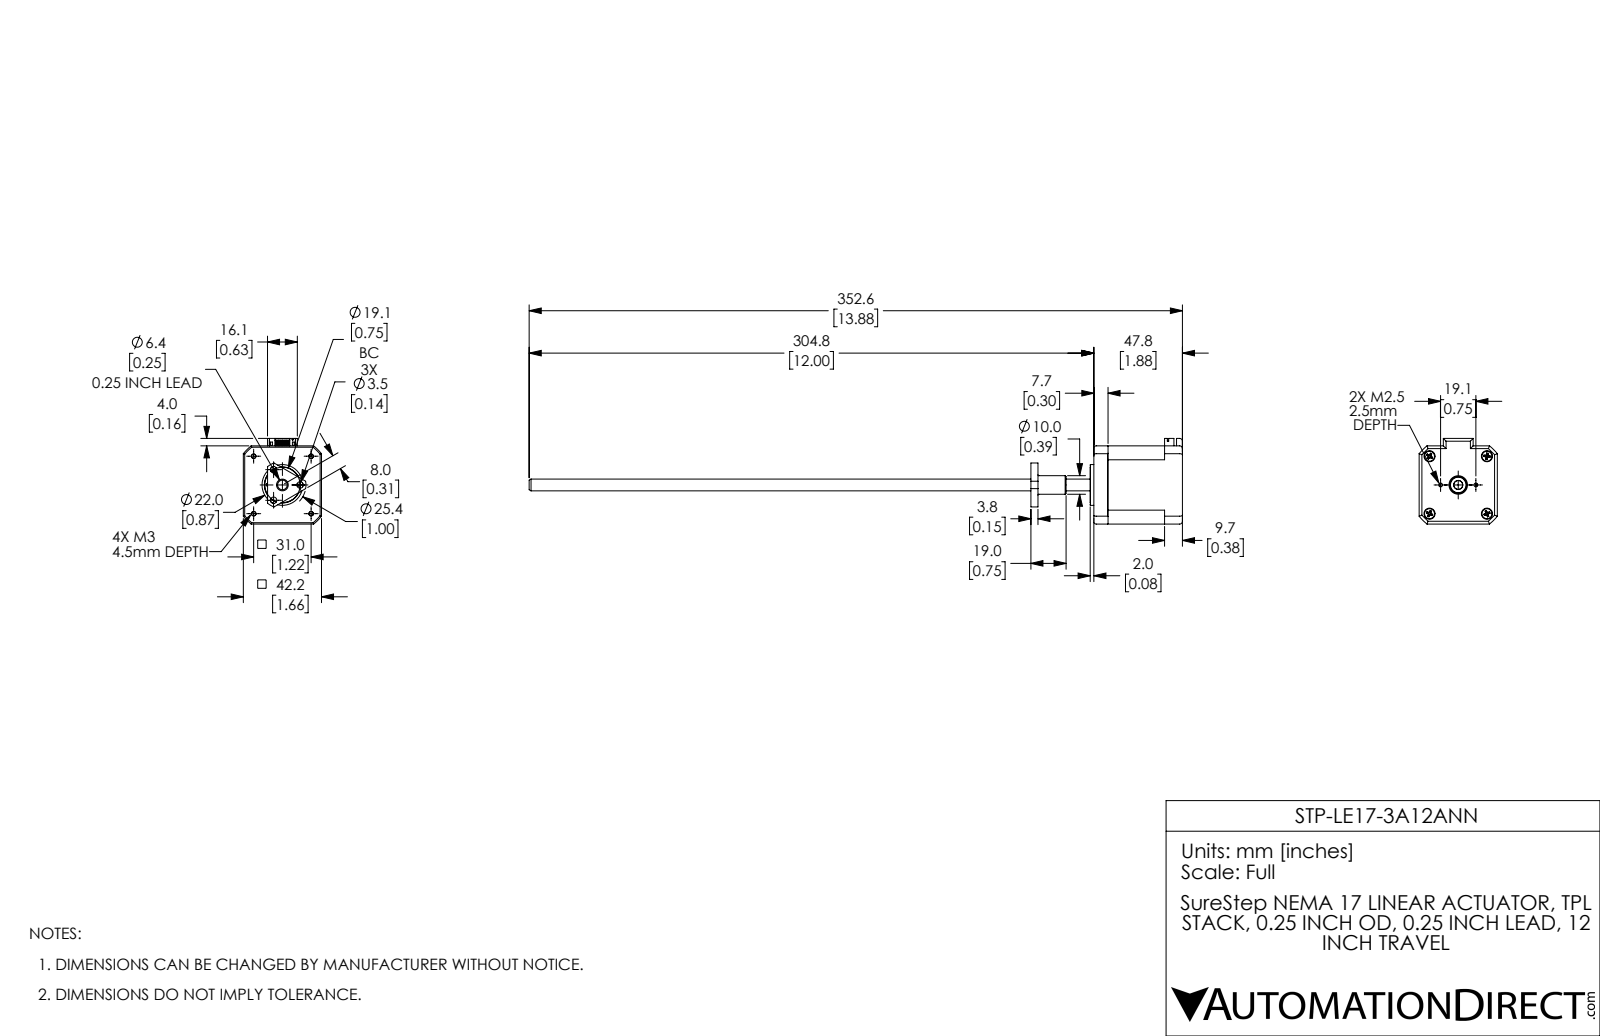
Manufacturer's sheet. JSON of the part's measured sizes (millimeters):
{"part_name": "STP-LE17-3A12ANN_1f; STP-LE17-3A12ANN; STP-LE17-3A12ANN_2", "step_written_by": "SolidWorks 2017 (AUTOMOTIVE_DESIGN)", "units": "millimeters", "bodies": {"solids": 5, "faces": 730, "planar": 364, "cylindrical": 236, "other": 130}, "overall_size": [352.6, 46.2, 42.2], "volume_mm3": 82923, "surface_area_mm2": 31393, "round_holes": [[2.5, 4], [3.8, 4], [6, 4], [3.5, 3], [1.5, 2], [2.05, 2], [4.9, 1], [13, 1], [17, 1], [19.46, 1], [20, 1]], "round_bosses_or_shafts": [[5.4, 4], [2.91, 4], [27, 1], [25.91, 1], [22, 1], [12, 1], [10, 1], [9, 1]], "partial_cylinders_radius": [[1, 12], [1.5, 11], [2.5, 2], [0.7, 1], [12.7, 1], [14.25, 1], [16, 1], [25.1, 1]], "face_to_face_distances": [42.2, 9.65, 47.8, 40.15, 38.15, 1.6, 30.5, 7.65, 45.3, 40.6], "hole_center_spacings": [16.61, 9.52, 21.92, 29.43, 31, 4.93, 8, 12.96]}
